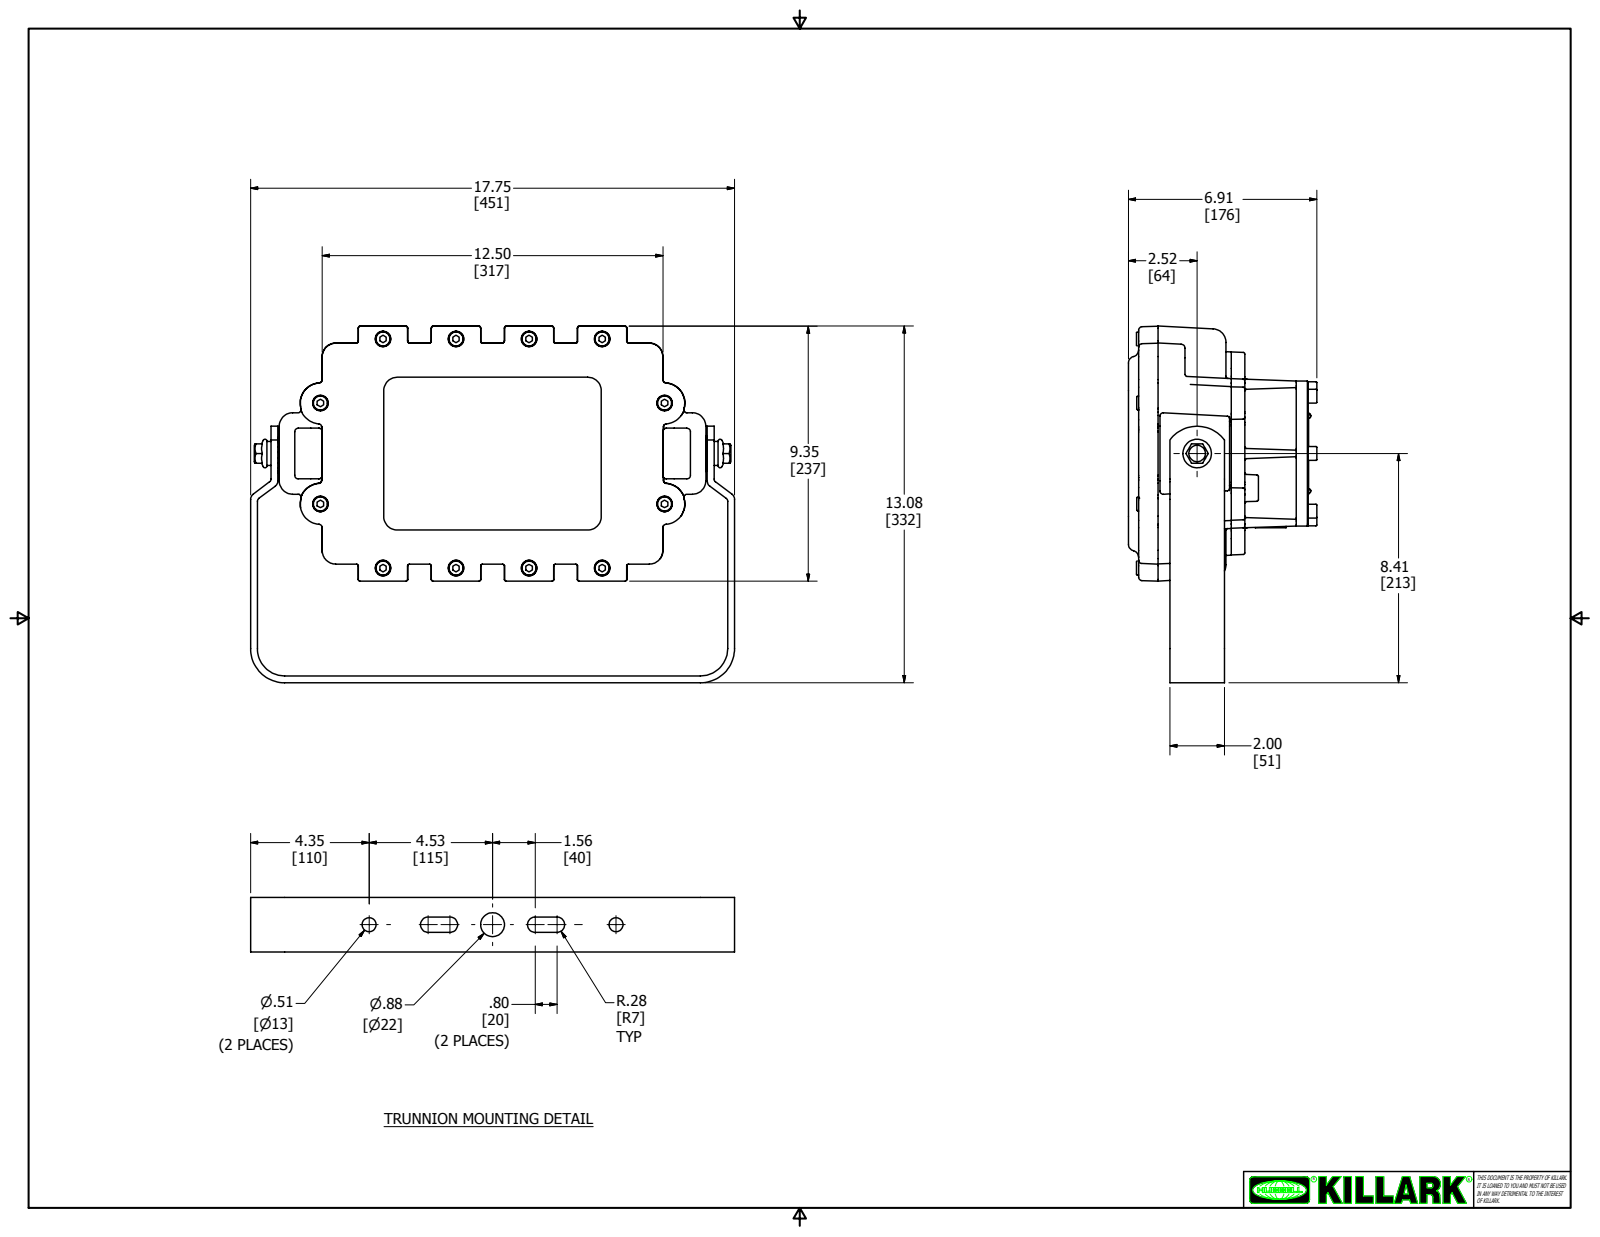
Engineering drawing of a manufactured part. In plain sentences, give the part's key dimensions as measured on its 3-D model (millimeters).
The part is named "23517M; 23279; LED-Nichia NVSW219CT; 2060-452_998-404_90 (+8 more)". Its 3-D file was written by "Autodesk Inventor 2016 (AUTOMOTIVE_DESIGN)". It is 598 solids with 73844 faces: 28171 planar, 2991 cylindrical and 42682 other. Overall it measures 450.85 by 332.28 by 175.51 millimeters. Its volume is 9 021 000 cubic millimeters and its surface area 2 276 000 square millimeters. Round holes: 180 of diameter 2.26, 45 of diameter 3.83, 45 of diameter 4.02, 45 of diameter 4.18, 30 of diameter 19.05, 29 of diameter 6.65, 15 of diameter 3.17, 15 of diameter 3.66, 12 of diameter 5.2, 12 of diameter 8.99, 8 of diameter 8.41, 8 of diameter 12. Round bosses or shafts: 180 of diameter 2, 75 of diameter 0.36, 45 of diameter 0.25, 6 of diameter 5.38, 6 of diameter 5.12, 6 of diameter 4.85, 4 of diameter 6, 4 of diameter 3. Partial cylindrical surfaces (rounded edges, fillets, slot ends): 178 of radius 1.59, 150 of radius 9.02, 72 of radius 2.03, 46 of radius 3.17, 45 of radius 7.07, 36 of radius 0.13, 24 of radius 0.76, 17 of radius 0.2. The main face-to-face distances are 1.59, 55.68, 10.78, 12.37, 12.7, 58.84, 69.62, 57.25, 68.05, 1.57. The hole center spacings are 39.42, 27.3, 68.05, 97.53, 138.81, 186.06, 198.11, 230.52.
